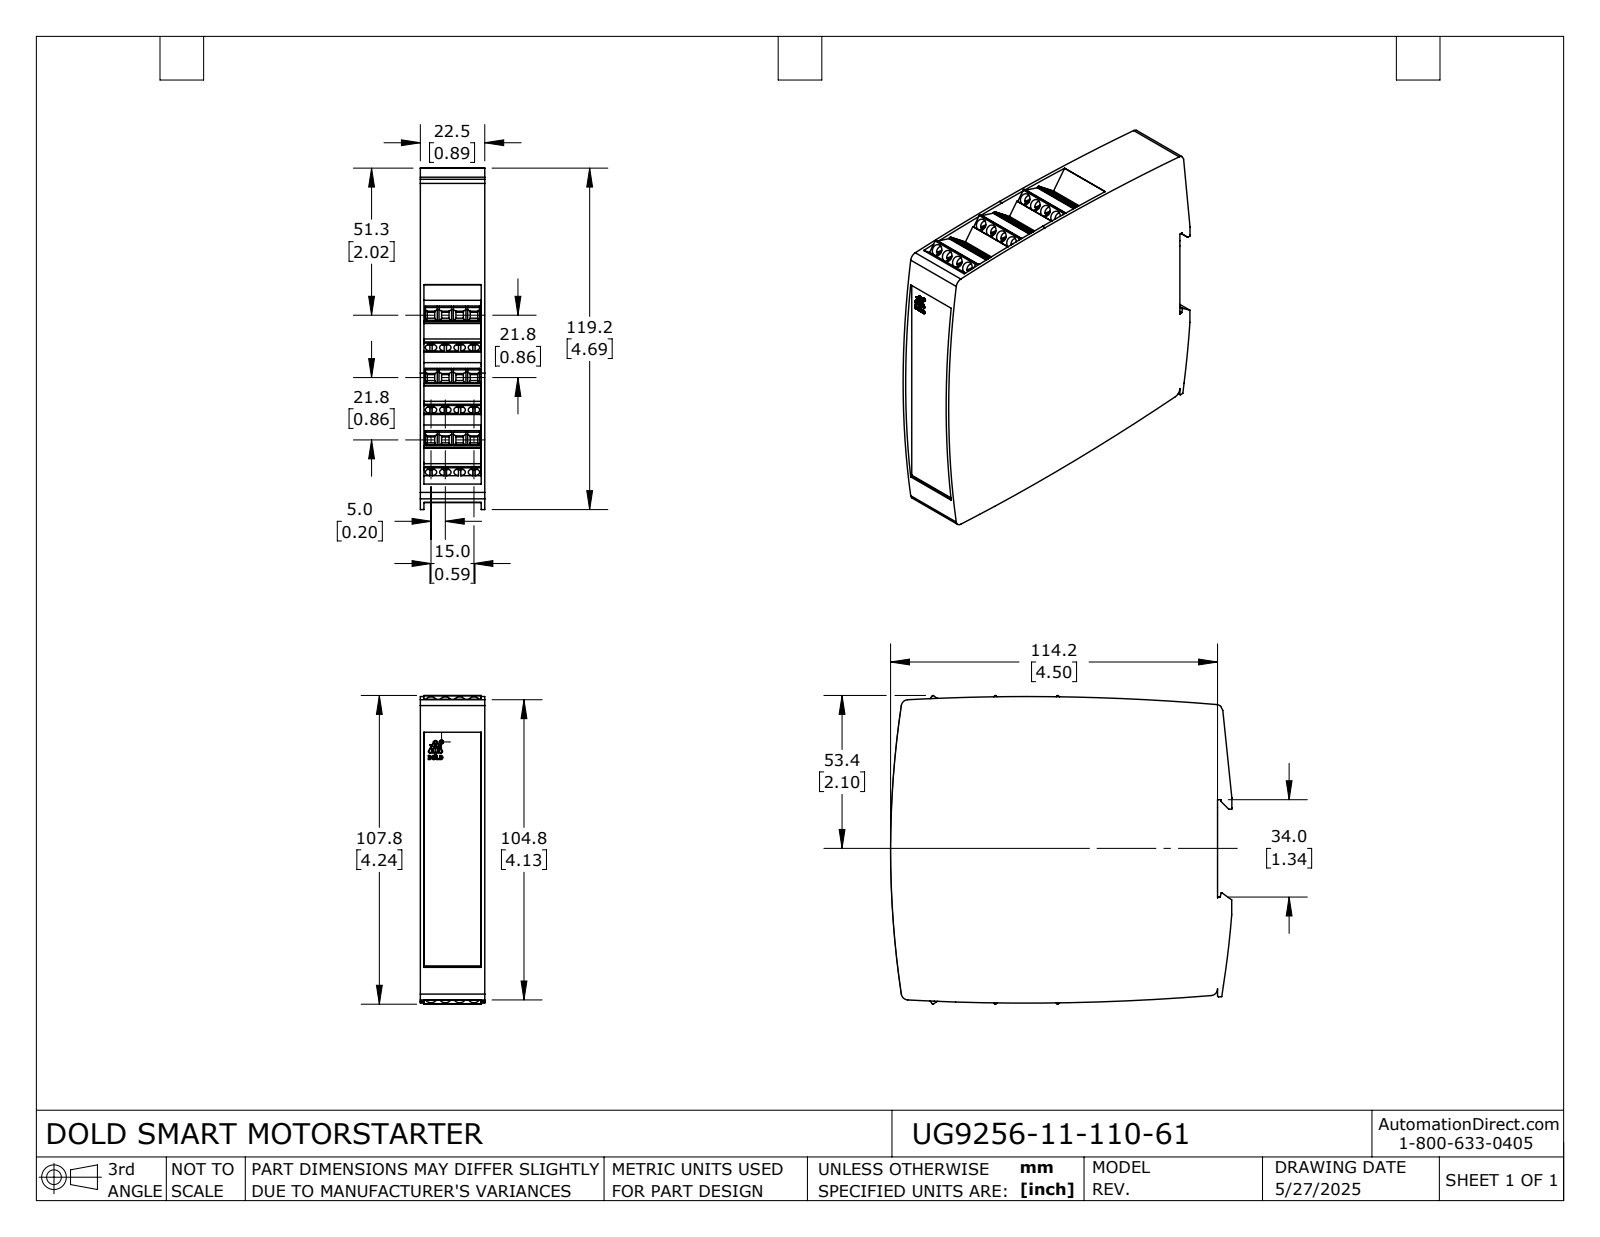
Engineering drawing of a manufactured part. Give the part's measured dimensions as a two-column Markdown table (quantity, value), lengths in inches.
| quantity | value |
| --- | --- |
| part name | UG9256-11-110-61 |
| STEP written by | SolidWorks 2024 (AUTOMOTIVE_DESIGN) |
| units | inches |
| bodies | 1 solid, 1036 faces (813 planar, 222 cylindrical, 1 other) |
| overall size | 4.693 × 4.243 × 0.886 |
| volume | 15.85 in³ |
| surface area | 64.72 in² |
| round holes (diameter × count) | 0.157 × 24, 0.053 × 1 |
| round bosses / shafts (diameter × count) | 0.15 × 24, 0.049 × 1 |
| partial cylindrical surfaces (radius × count) | 0.012 × 15, 0.02 × 14, 0.004 × 12, 0.094 × 7, 0.005 × 6, 0.004 × 4, 31.496 × 4, 0.021 × 3 |
| main face-to-face distances | 0.886, 0.049, 0.837, 0.675, 4.379, 0.051, 0.835, 1.35, 0.528, 0.785 |
| hole center spacings | 0.563, 0.197, 0.528, 0.658, 0.394, 1.073, 0.792, 1.055 |
